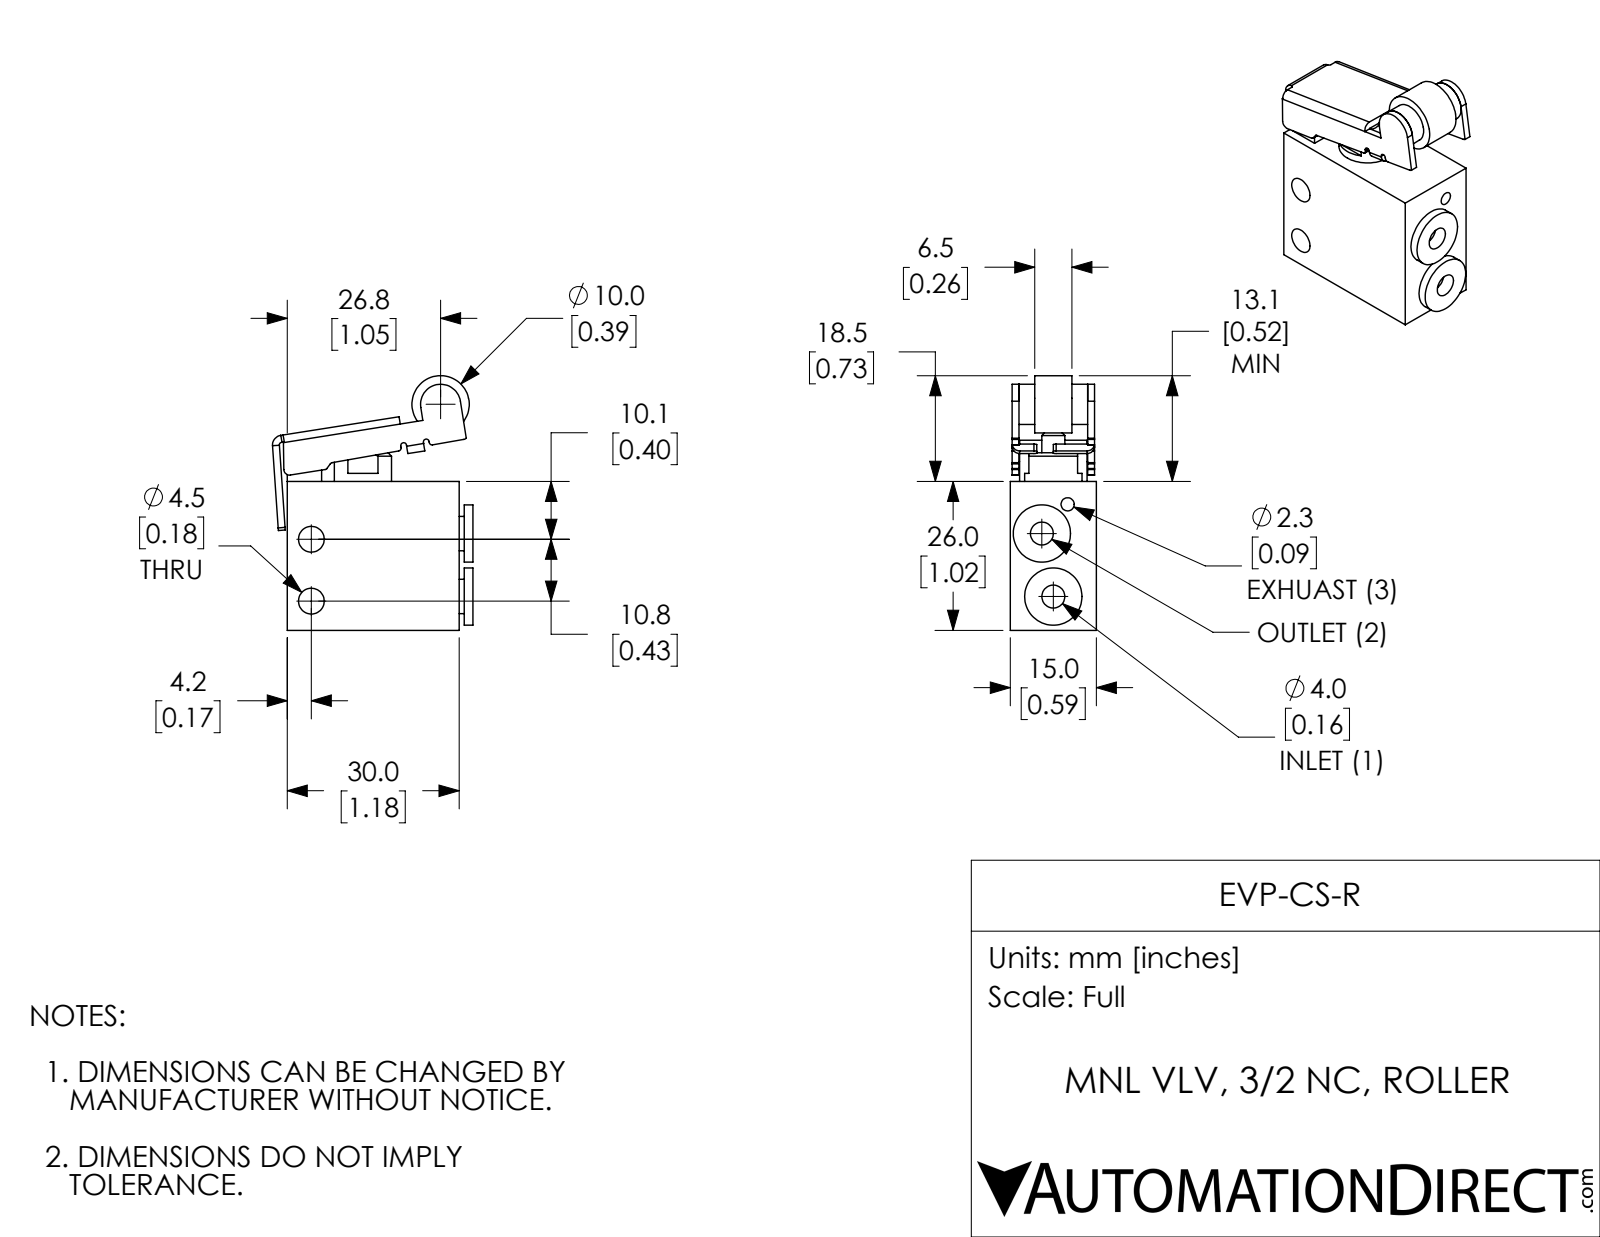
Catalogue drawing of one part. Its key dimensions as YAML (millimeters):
part_name: "EVP-CS-R"
step_written_by: "SolidWorks 2017 (AUTOMOTIVE_DESIGN)"
units: millimeters
bodies: {solids: 3, faces: 149, planar: 75, cylindrical: 70, other: 4}
overall_size: [44.5, 35, 15]
volume: 14300
surface_area: 7232
round_holes:
  - {diameter: 4, count: 3}
  - {diameter: 4.5, count: 2}
  - {diameter: 2.3, count: 1}
  - {diameter: 3.1, count: 1}
round_bosses_or_shafts:
  - {diameter: 10, count: 4}
  - {diameter: 6, count: 2}
  - {diameter: 7, count: 1}
  - {diameter: 5, count: 1}
  - {diameter: 4, count: 1}
partial_cylinders:
  - {radius: 0.5, count: 13}
  - {radius: 1.3, count: 4}
  - {radius: 0.1, count: 2}
  - {radius: 0.4, count: 2}
  - {radius: 1, count: 2}
  - {radius: 1.7, count: 1}
face_to_face_distances: [15, 1.2, 1.5, 13.5, 14.7, 13.2, 30, 26, 1.2, 12]
hole_center_spacings: [6.8, 10.8, 11.2, 15.2, 16.3, 25.9]
